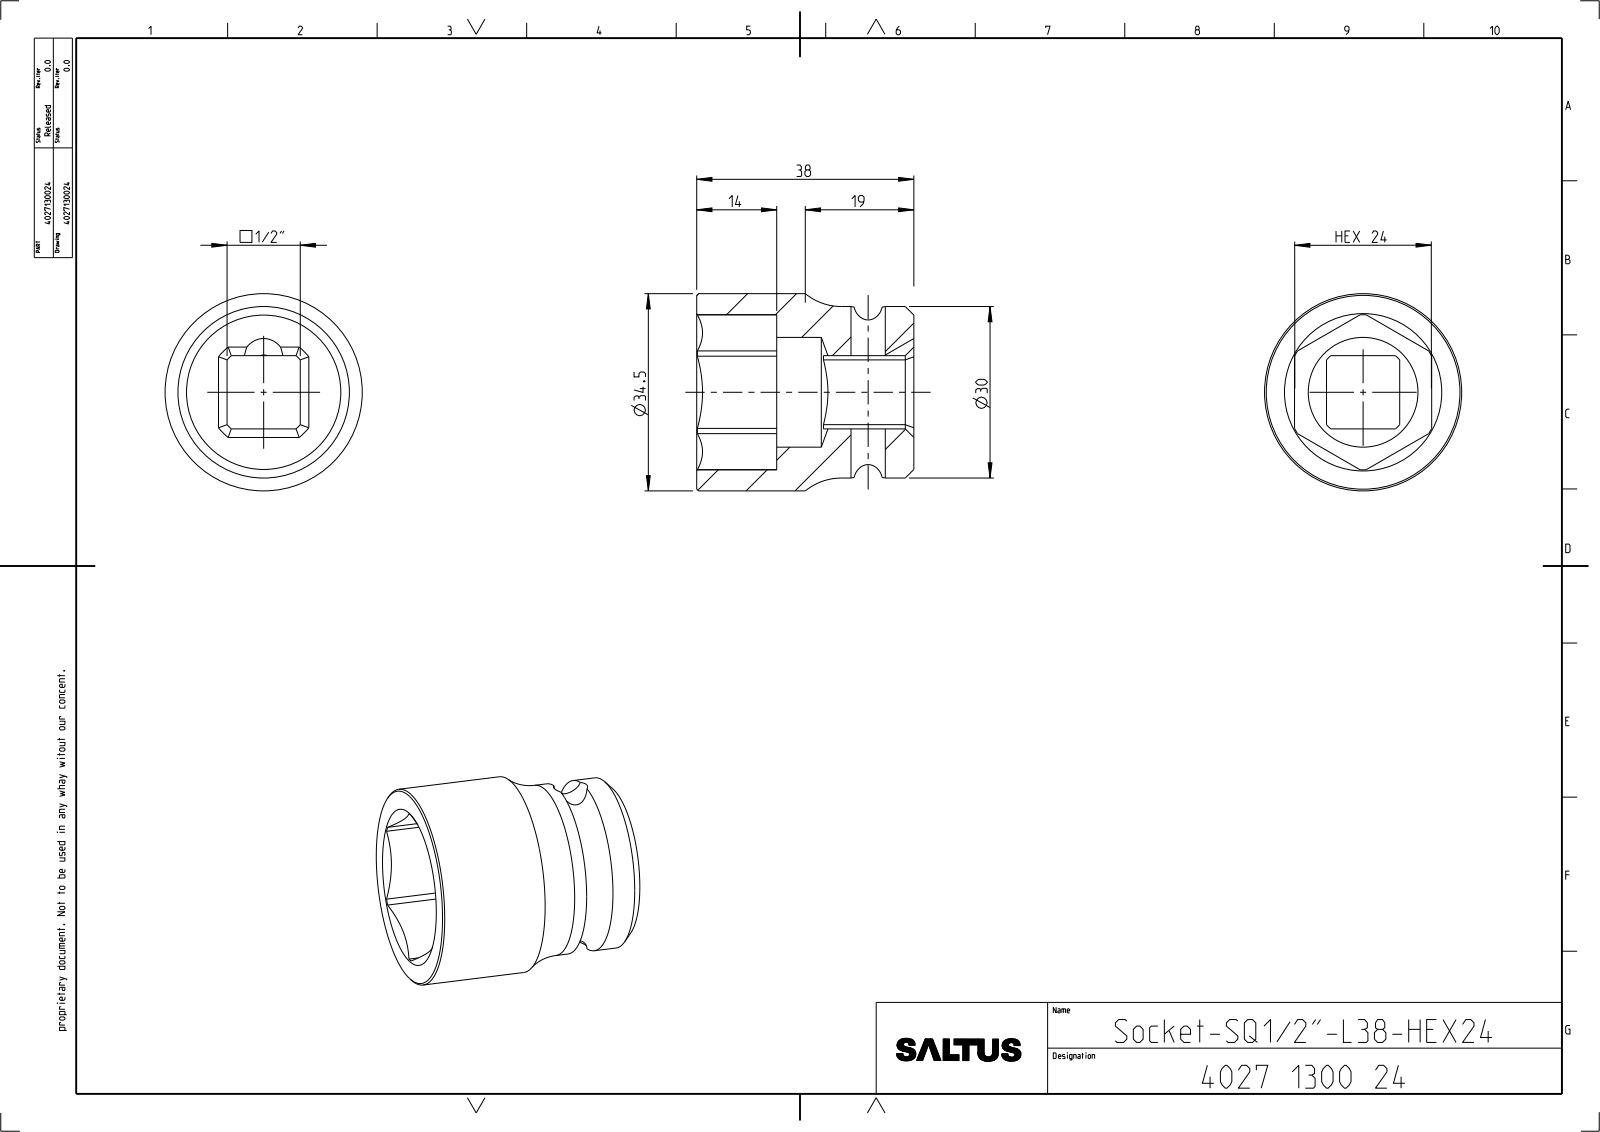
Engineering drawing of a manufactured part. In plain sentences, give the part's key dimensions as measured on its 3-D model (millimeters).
The part is named "4027130024". Its 3-D file was written by "CREO PARAMETRIC BY PTC INC, 2022414 (CONFIG_CONTROL_DESIGN)". It is 1 solid with 57 faces: 18 planar, 23 cylindrical and 16 other. Overall it measures 38 by 34.5 by 34.5 millimeters. Its volume is 18 421 cubic millimeters and its surface area 7 733 square millimeters. Round holes: 1 of diameter 6, 1 of diameter 19.2. Round bosses or shafts: 1 of diameter 34.5, 1 of diameter 30. Partial cylindrical surfaces (rounded edges, fillets, slot ends): 1 of radius 4, 1 of radius 8.55, 1 of radius 13.56. The main face-to-face distances are 24, 5.59, 18.41, 38, 12.82, 14.
